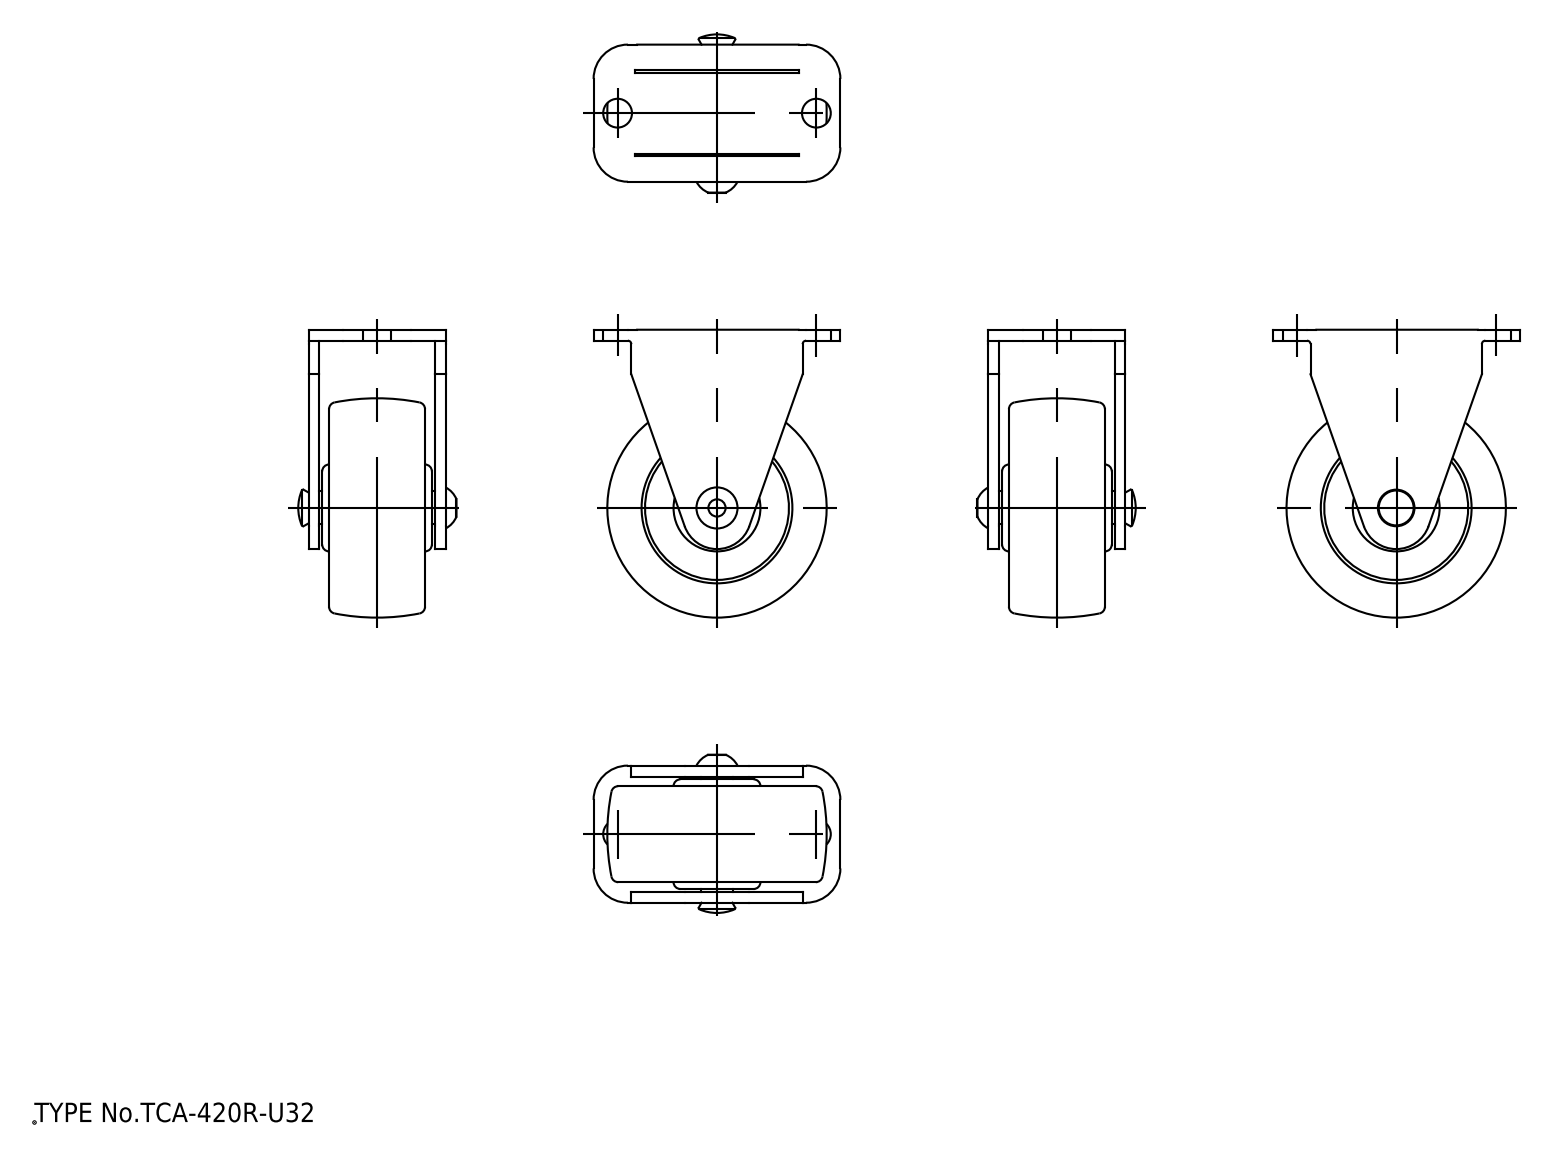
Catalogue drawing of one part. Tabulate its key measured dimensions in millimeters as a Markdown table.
| quantity | value |
| --- | --- |
| part name | wheel; axle |
| STEP written by | spGate 19.8.4 (****-****-****-****) (AUTOMOTIVE_DESIGN) |
| units | millimeters |
| bodies | 3 solids, 86 faces (34 planar, 22 cylindrical, 30 other) |
| overall size | 42 × 36 × 23.09 |
| volume | 13 670 mm³ |
| surface area | 7 280 mm² |
| round holes (diameter × count) | 4.2 × 2, 4.8 × 1 |
| round bosses / shafts (diameter × count) | 12.68 × 1 |
| partial cylindrical surfaces (radius × count) | 5 × 5 |
| main face-to-face distances | 1.6, 18.4, 3, 17, 1.4, 15.4, 20, 16.8, 0.5, 3.5 |
| hole center spacings | 29 |
